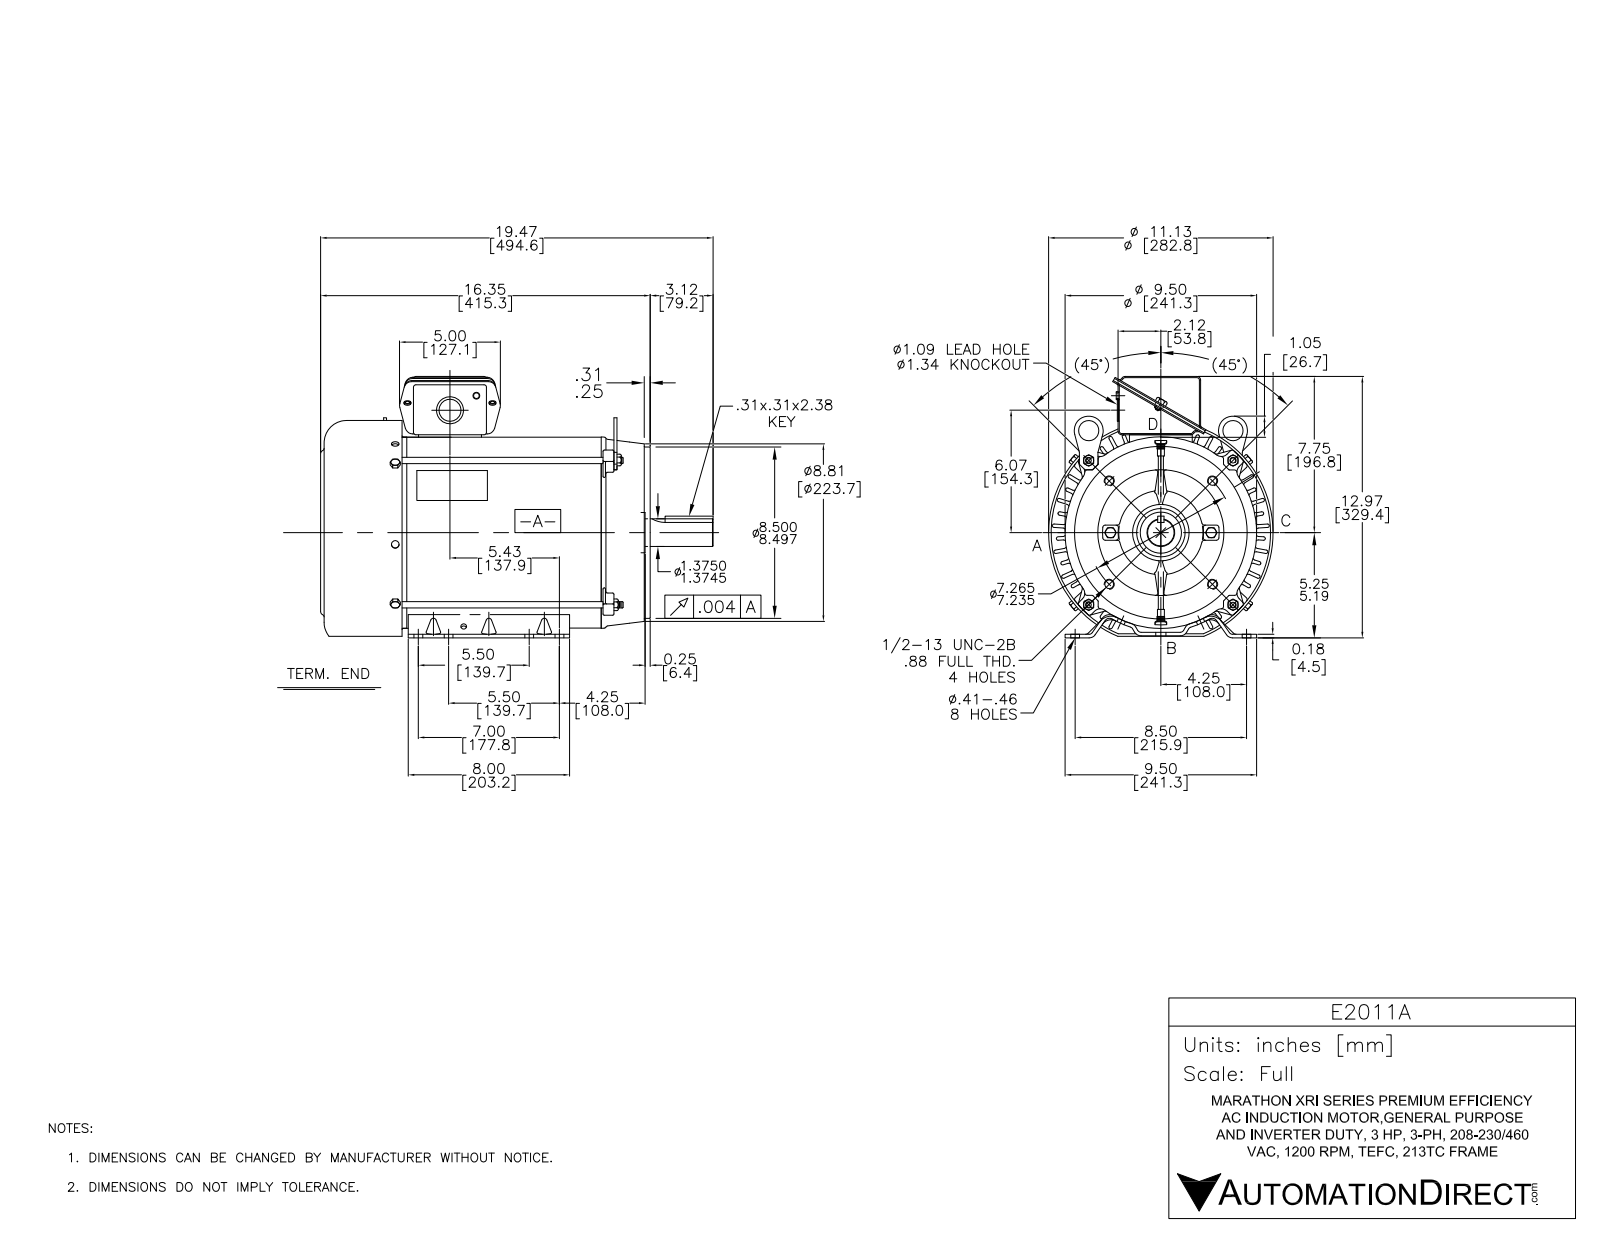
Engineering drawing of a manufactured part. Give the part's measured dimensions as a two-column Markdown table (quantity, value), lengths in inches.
| quantity | value |
| --- | --- |
| part name | E2011A r2 |
| STEP written by | SolidWorks 2017 (AUTOMOTIVE_DESIGN) |
| units | inches |
| bodies | 30 solids, 3325 faces (1051 planar, 1045 cylindrical, 1229 other) |
| overall size | 19.466 × 12.914 × 11.16 |
| volume | 171.7 in³ |
| surface area | 1 997 in² |
| round holes (diameter × count) | 0.373 × 10, 0.257 × 4, 0.32 × 4, 0.37 × 4, 0.422 × 4, 0.435 × 4, 0.435 × 4, 0.219 × 3, 0.267 × 3, 0.176 × 2, 0.218 × 2, 0.279 × 2 |
| round bosses / shafts (diameter × count) | 0.31 × 10, 0.44 × 6, 0.399 × 2, 0.295 × 2, 0.19 × 2, 9.489 × 1, 9.271 × 1, 8.499 × 1 |
| partial cylindrical surfaces (radius × count) | 0.13 × 149, 0.06 × 134, 0.12 × 86, 0.25 × 34, 0.03 × 12, 0.18 × 10, 0.04 × 8, 0.14 × 8 |
| main face-to-face distances | 0.06, 0.17, 16.175, 0.12, 0.179, 0.1, 2.734, 16.345, 0.179, 0.11 |
| hole center spacings | 6.224, 2.5, 7.156, 1, 1.435, 1.5, 2.564, 3.5 |
